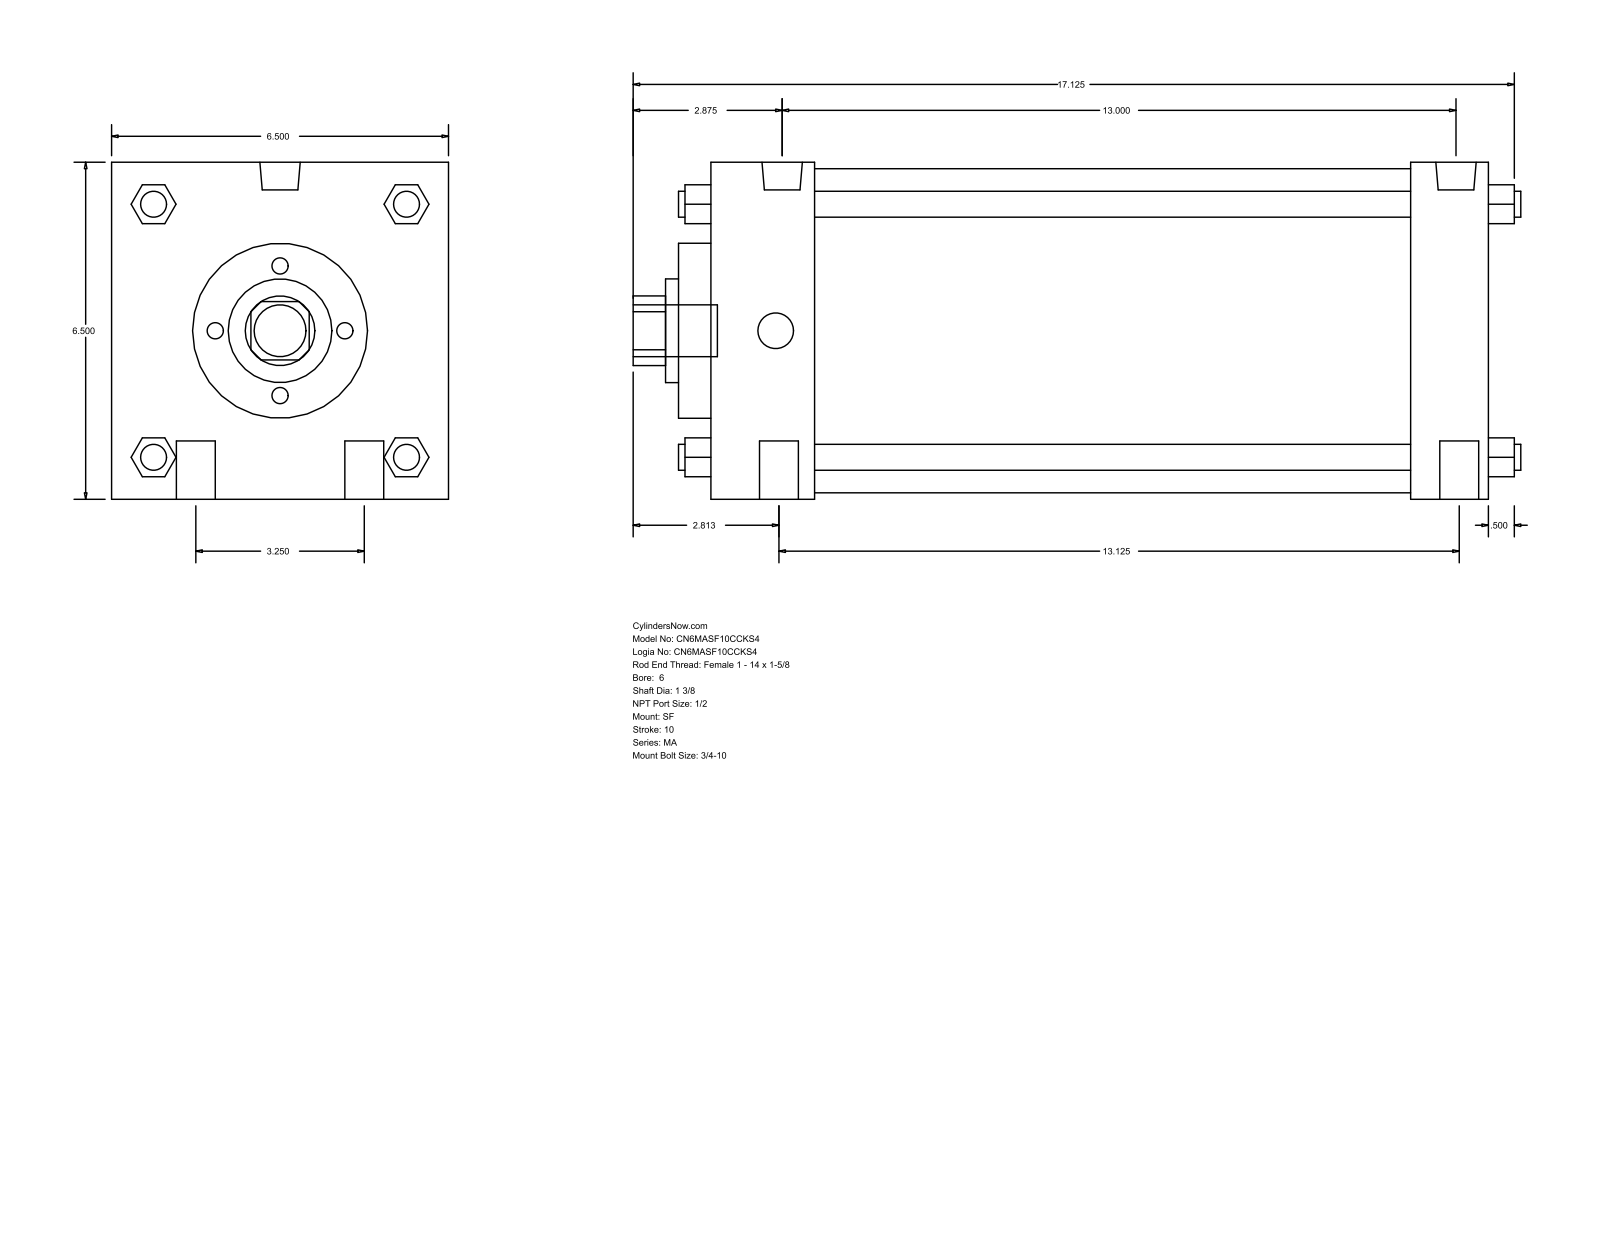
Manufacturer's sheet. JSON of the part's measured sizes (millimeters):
{"part_name": "MA_SF__0600_1.375", "step_written_by": "GSSL Pune (CONFIG_CONTROL_DESIGN)", "units": "millimeters", "bodies": {"solids": 0, "faces": 126, "planar": 95, "cylindrical": 31, "other": 0}, "overall_size": [434.98, 165.1, 165.1], "round_holes": [[34.92, 1], [50.8, 1], [85.72, 1], [158.75, 1]], "round_bosses_or_shafts": [[19.05, 4], [12.7, 4], [19.77, 2], [17.46, 2], [25.4, 1]], "partial_cylinders_radius": [[17.06, 1]], "face_to_face_distances": [165.1, 381, 342.9, 50.8, 38.1, 292.1, 330.2, 15.87, 66.67, 358.77]}
